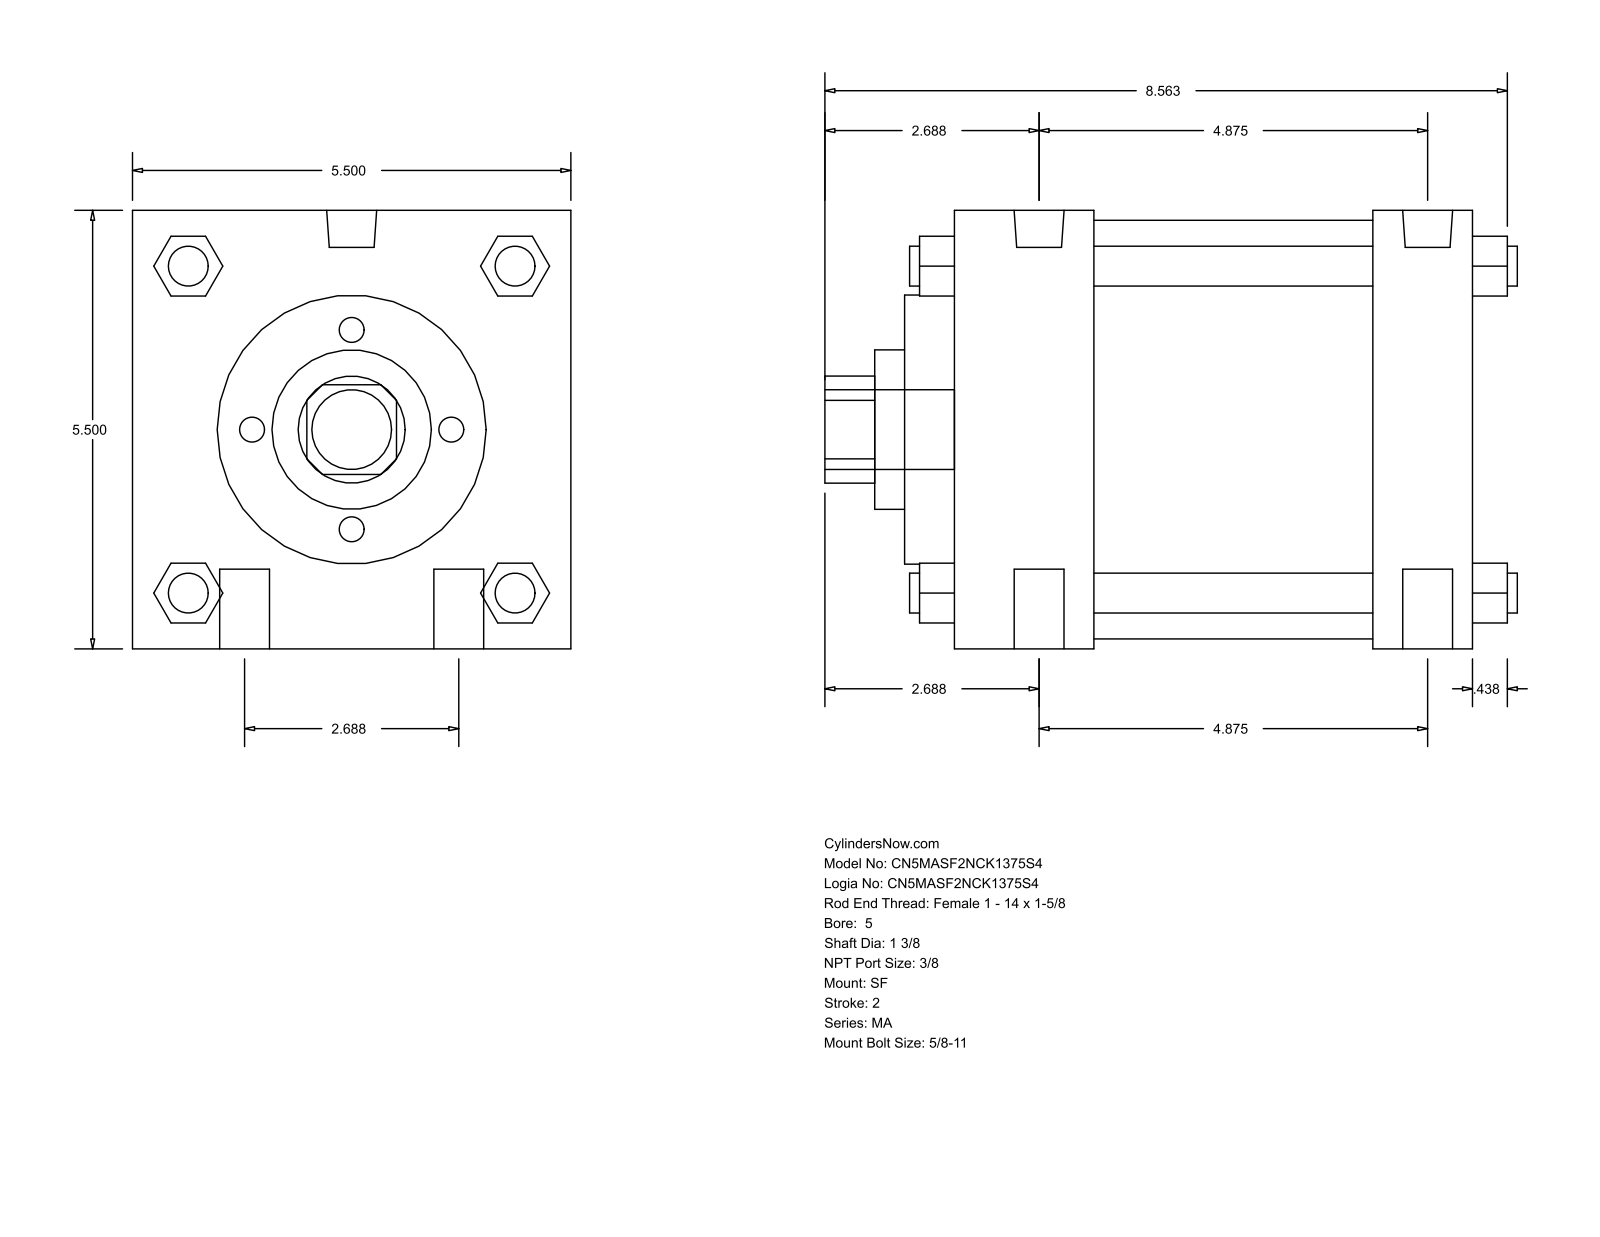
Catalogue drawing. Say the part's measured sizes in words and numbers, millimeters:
The part is named "MA_SF__0500_1.375". Its 3-D file was written by "GSSL Pune (CONFIG_CONTROL_DESIGN)". It is 0 solids with 126 faces: 95 planar, 31 cylindrical and 0 other. Overall it measures 220.66 by 139.7 by 139.7 millimeters. Round holes: 1 of diameter 34.92, 1 of diameter 50.8, 1 of diameter 85.72, 1 of diameter 133.35. Round bosses or shafts: 4 of diameter 15.88, 4 of diameter 12.7, 2 of diameter 15.93, 2 of diameter 11.11, 1 of diameter 25.4. Partial cylindrical surfaces (rounded edges, fillets, slot ends): 1 of radius 17.06. The main face-to-face distances are 139.7, 165.11, 44.45, 133.35, 88.9, 120.66, 31.76, 15.87, 60.32, 149.22.
